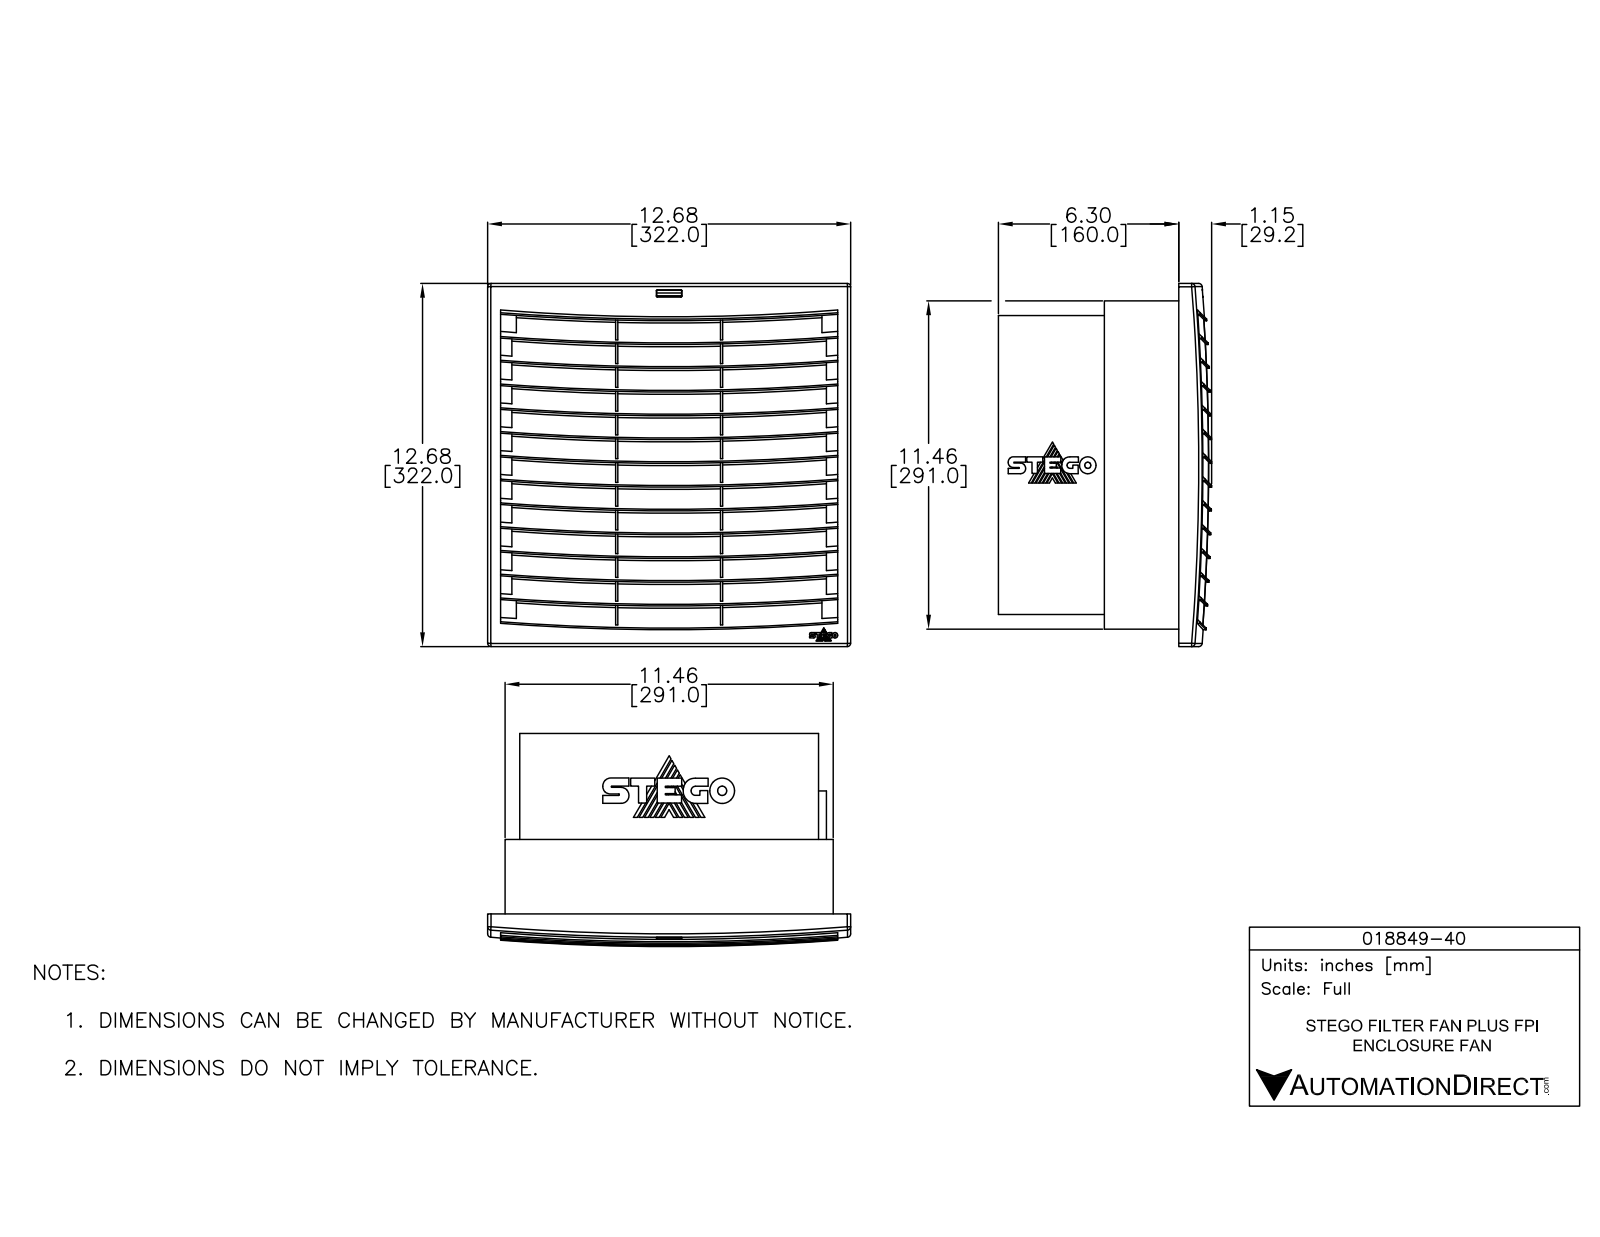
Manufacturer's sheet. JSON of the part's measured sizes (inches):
{"part_name": "018849-40", "step_written_by": "SolidWorks 2018 (AUTOMOTIVE_DESIGN)", "units": "inches", "bodies": {"solids": 1, "faces": 831, "planar": 477, "cylindrical": 354, "other": 0}, "overall_size": [12.677, 12.677, 7.441], "volume_in3": 276.7, "surface_area_in2": 1385, "round_holes": [[3, 1], [3.99, 1], [4.692, 1], [4.979, 1], [5.909, 1], [5.969, 1], [6.958, 1], [7.126, 1], [7.947, 1], [8.344, 1], [9.134, 1], [9.738, 1]], "round_bosses_or_shafts": [[11.389, 1], [10.846, 1], [10.738, 1], [8.698, 1], [8.341, 1], [7.481, 1], [7.352, 1], [6.362, 1]], "partial_cylinders_radius": [[64.96, 23], [4.43, 7], [0.276, 4], [0.343, 4], [1.217, 1], [1.737, 1], [1.914, 1], [44.216, 1]], "face_to_face_distances": [0.636, 1.272, 1.909, 2.545, 0.197, 0.059, 3.181, 0.287, 11.17, 0.695]}
